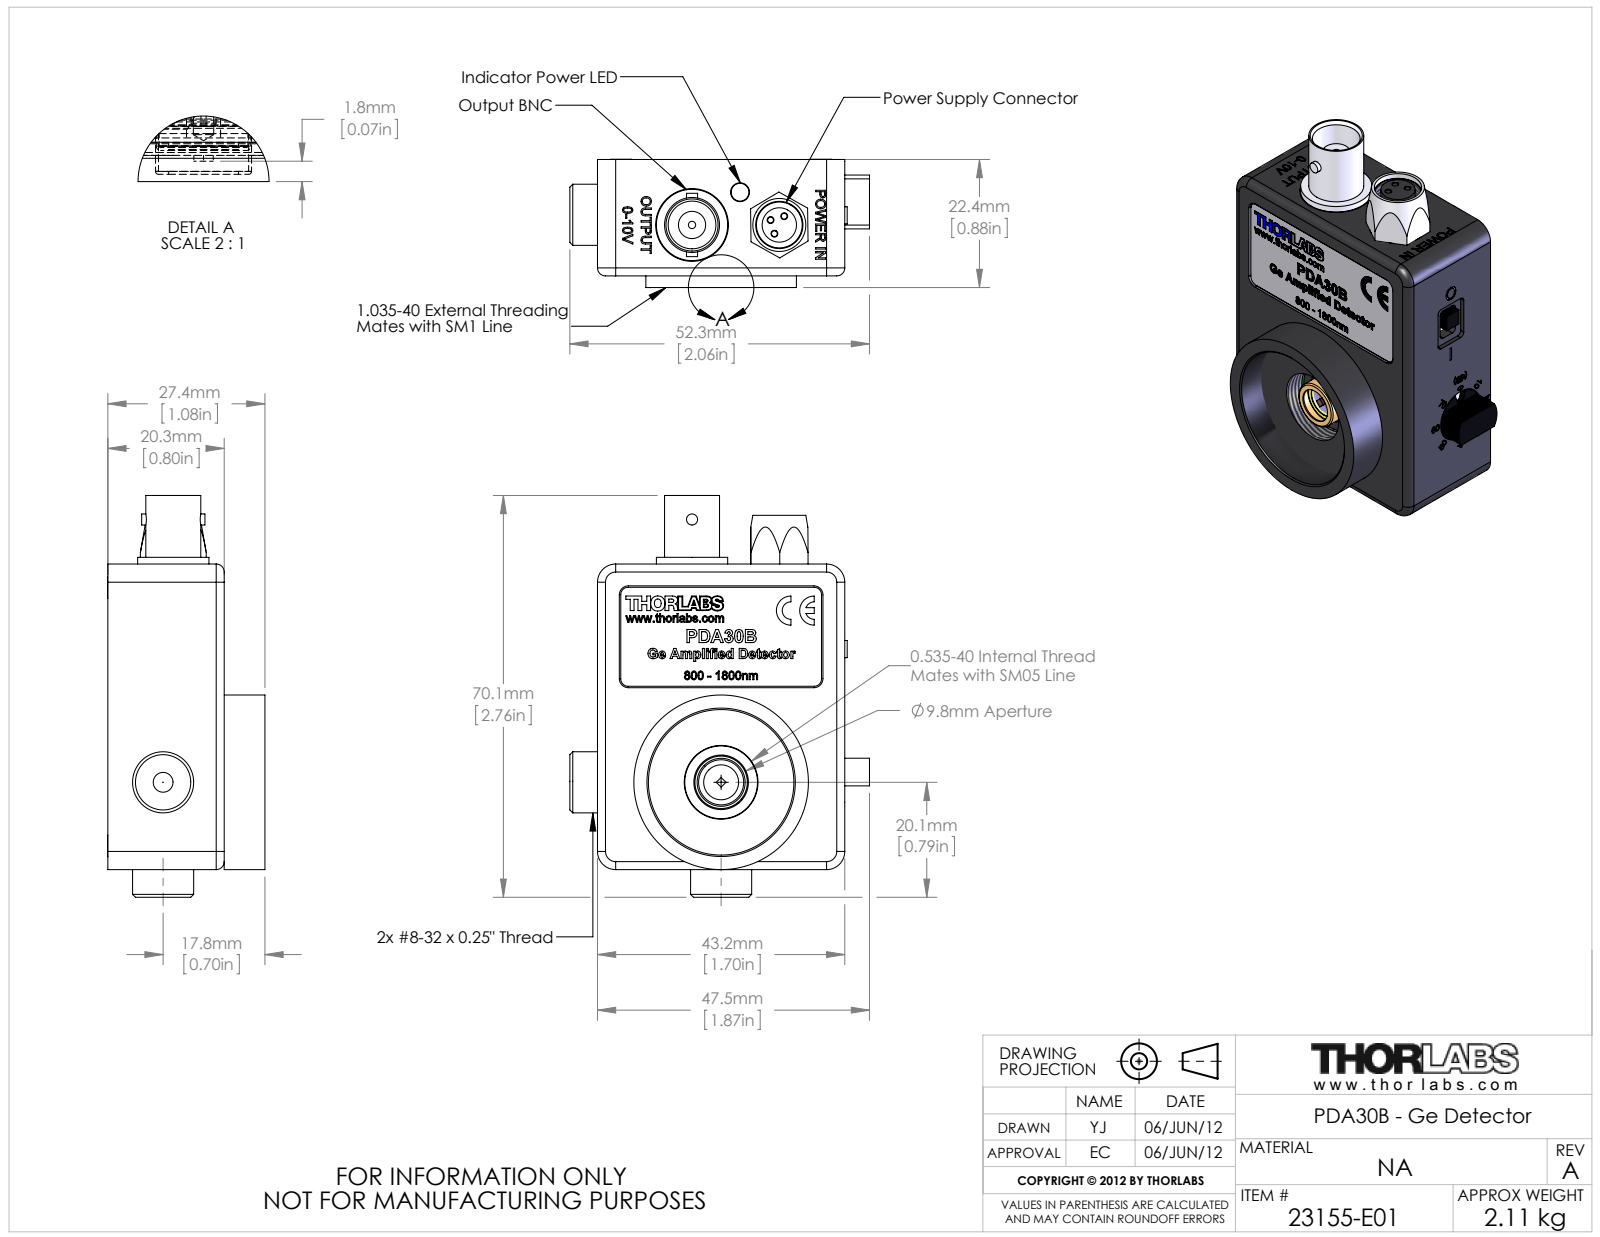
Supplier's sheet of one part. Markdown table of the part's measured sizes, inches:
| quantity | value |
| --- | --- |
| part name | Board; 23155-002_PDA30B-LB1; 13053-001_Etching; pcb (+8 more) |
| STEP written by | SolidWorks 2011 (AUTOMOTIVE_DESIGN) |
| units | inches |
| bodies | 25 solids, 2305 faces (1153 planar, 378 cylindrical, 774 other) |
| overall size | 2.761 × 2.06 × 1.082 |
| volume | 1.571 in³ |
| surface area | 49.56 in² |
| round holes (diameter × count) | 0.037 × 9, 0.032 × 8, 0.07 × 7, 0.096 × 7, 0.033 × 6, 0.125 × 4, 0.2 × 4, 0.028 × 3, 0.03 × 3, 0.039 × 3, 0.05 × 3, 0.065 × 2 |
| round bosses / shafts (diameter × count) | 0.086 × 7, 0.02 × 6, 0.147 × 4, 0.14 × 3, 0.016 × 3, 0.42 × 2, 0.37 × 2, 0.236 × 2 |
| partial cylindrical surfaces (radius × count) | 0.125 × 23, 0.031 × 14, 0.095 × 8, 0.005 × 4, 0.05 × 4, 0.055 × 4, 0.024 × 3, 0.062 × 3 |
| main face-to-face distances | 0.063, 0.502, 0.565, 0.1, 0.502, 0.439, 0.063, 0.05, 0.07, 0.165 |
| hole center spacings | 0.1, 0.141, 0.079, 0.126, 0.128, 0.2, 0.203, 0.28 |
